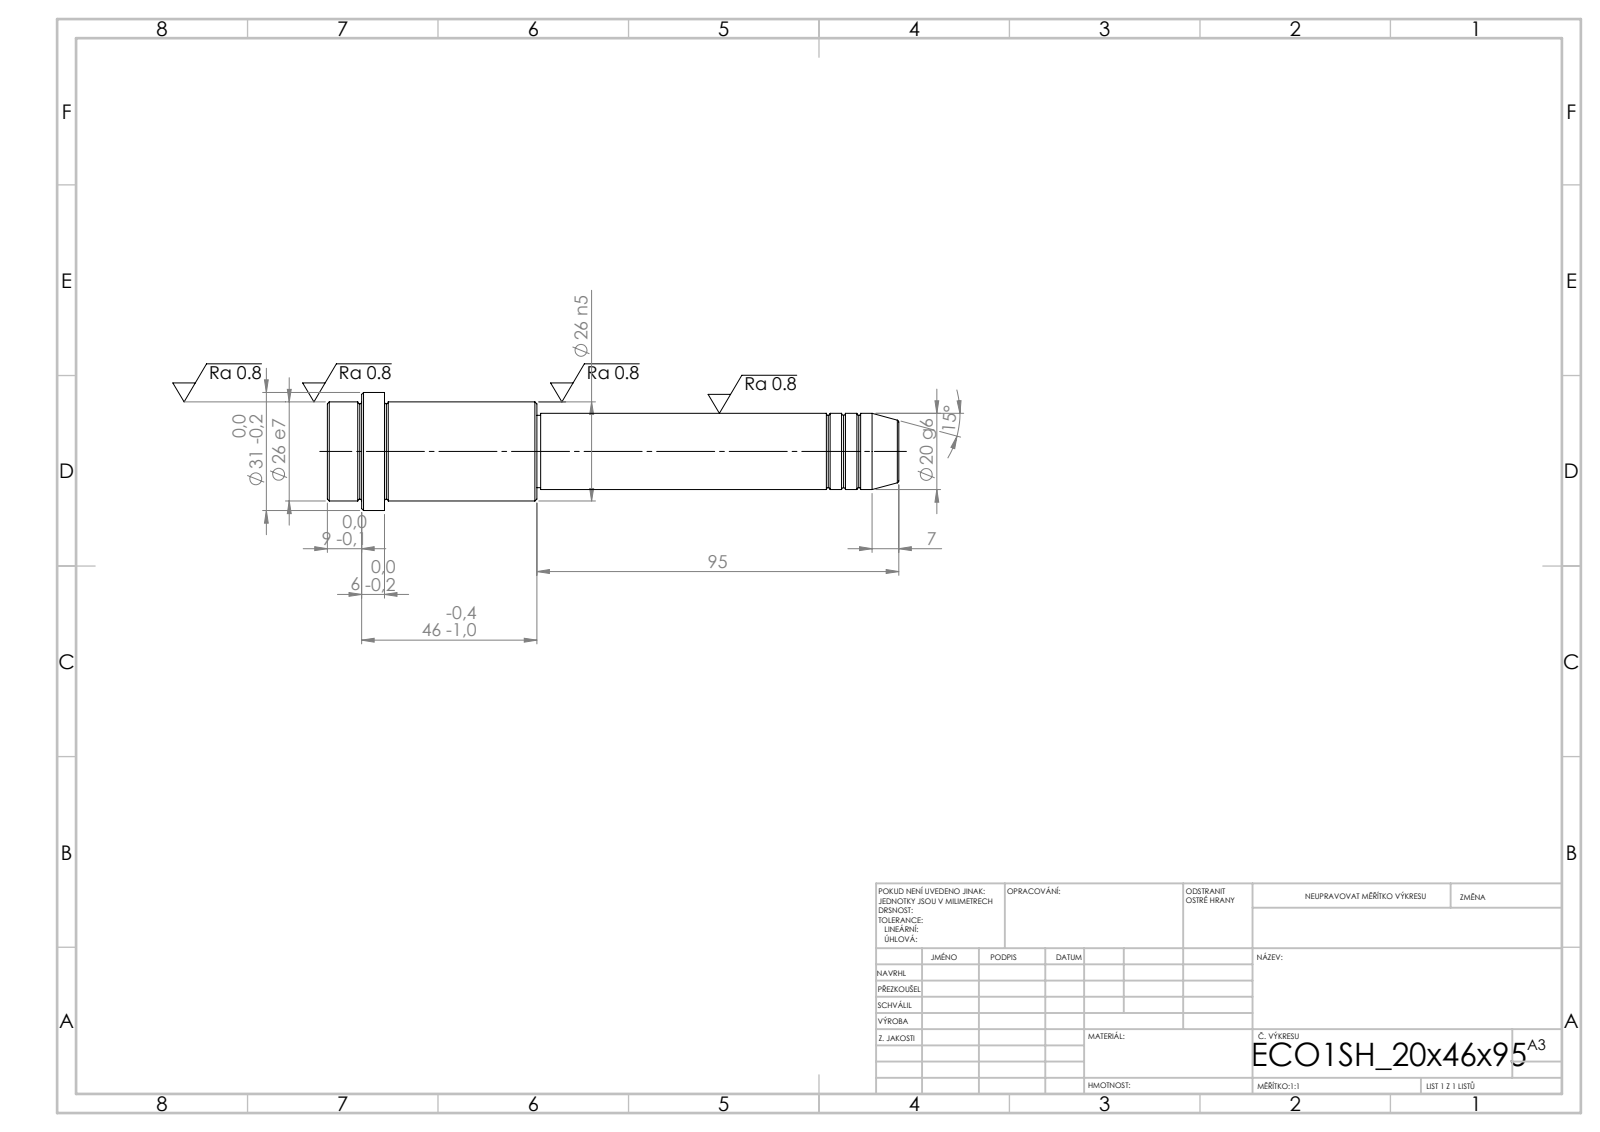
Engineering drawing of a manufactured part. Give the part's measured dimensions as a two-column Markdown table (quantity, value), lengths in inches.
| quantity | value |
| --- | --- |
| STEP written by | SolidWorks 2019 (CONFIG_CONTROL_DESIGN) |
| units | inches |
| bodies | 1 solid, 52 faces (6 planar, 16 cylindrical, 30 other) |
| overall size | 5.906 × 1.22 × 1.22 |
| volume | 3.649 in³ |
| surface area | 18.74 in² |
| round bosses / shafts (diameter × count) | 1.22 × 1, 1.024 × 1, 0.787 × 1, 0.748 × 1 |
| main face-to-face distances | 0.591, 1.575, 2.165, 3.74, 5.315, 5.906, 5.551, 1.811, 0.236, 0.354 |
